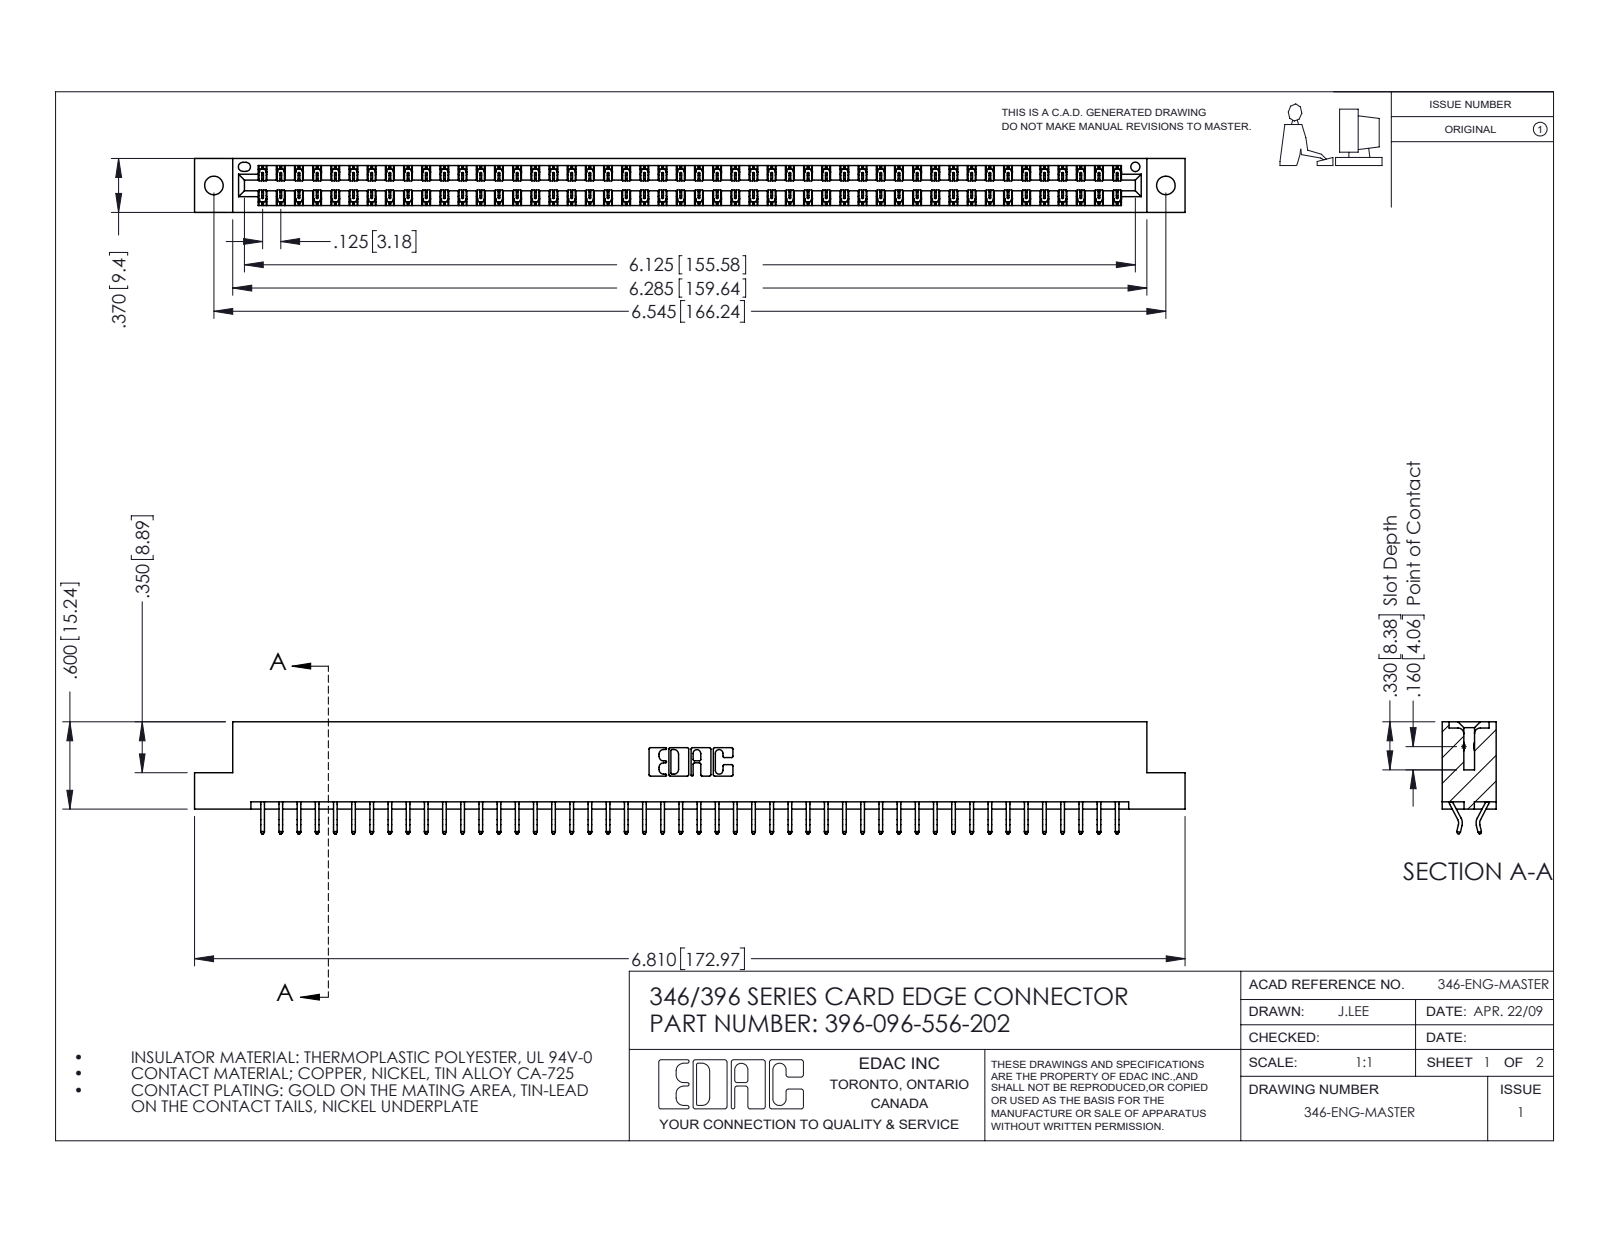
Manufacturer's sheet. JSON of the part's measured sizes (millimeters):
{"part_name": "346 Part_Flush Mounting Lugs - 0.128 Dia; 396-096-556-202; 345-292-001_556 Tail", "step_written_by": "SolidWorks 2016 (CONFIG_CONTROL_DESIGN)", "units": "millimeters", "bodies": {"solids": 97, "faces": 5690, "planar": 3820, "cylindrical": 1870, "other": 0}, "overall_size": [173, 19.6, 9.4], "volume_mm3": 16880, "surface_area_mm2": 22930, "round_holes": [[3.3, 2], [1.6, 1]], "partial_cylinders_radius": [[0.2, 144], [0.3, 22], [0.2, 6], [0.8, 6], [0.7, 3], [0.3, 2], [0.4, 2], [0.6, 2]], "face_to_face_distances": [1.2, 8.2, 9.4, 6.4, 0.6, 1.8, 7.6, 7, 3.8, 5.6], "hole_center_spacings": [6.2, 160.9, 166.2]}
